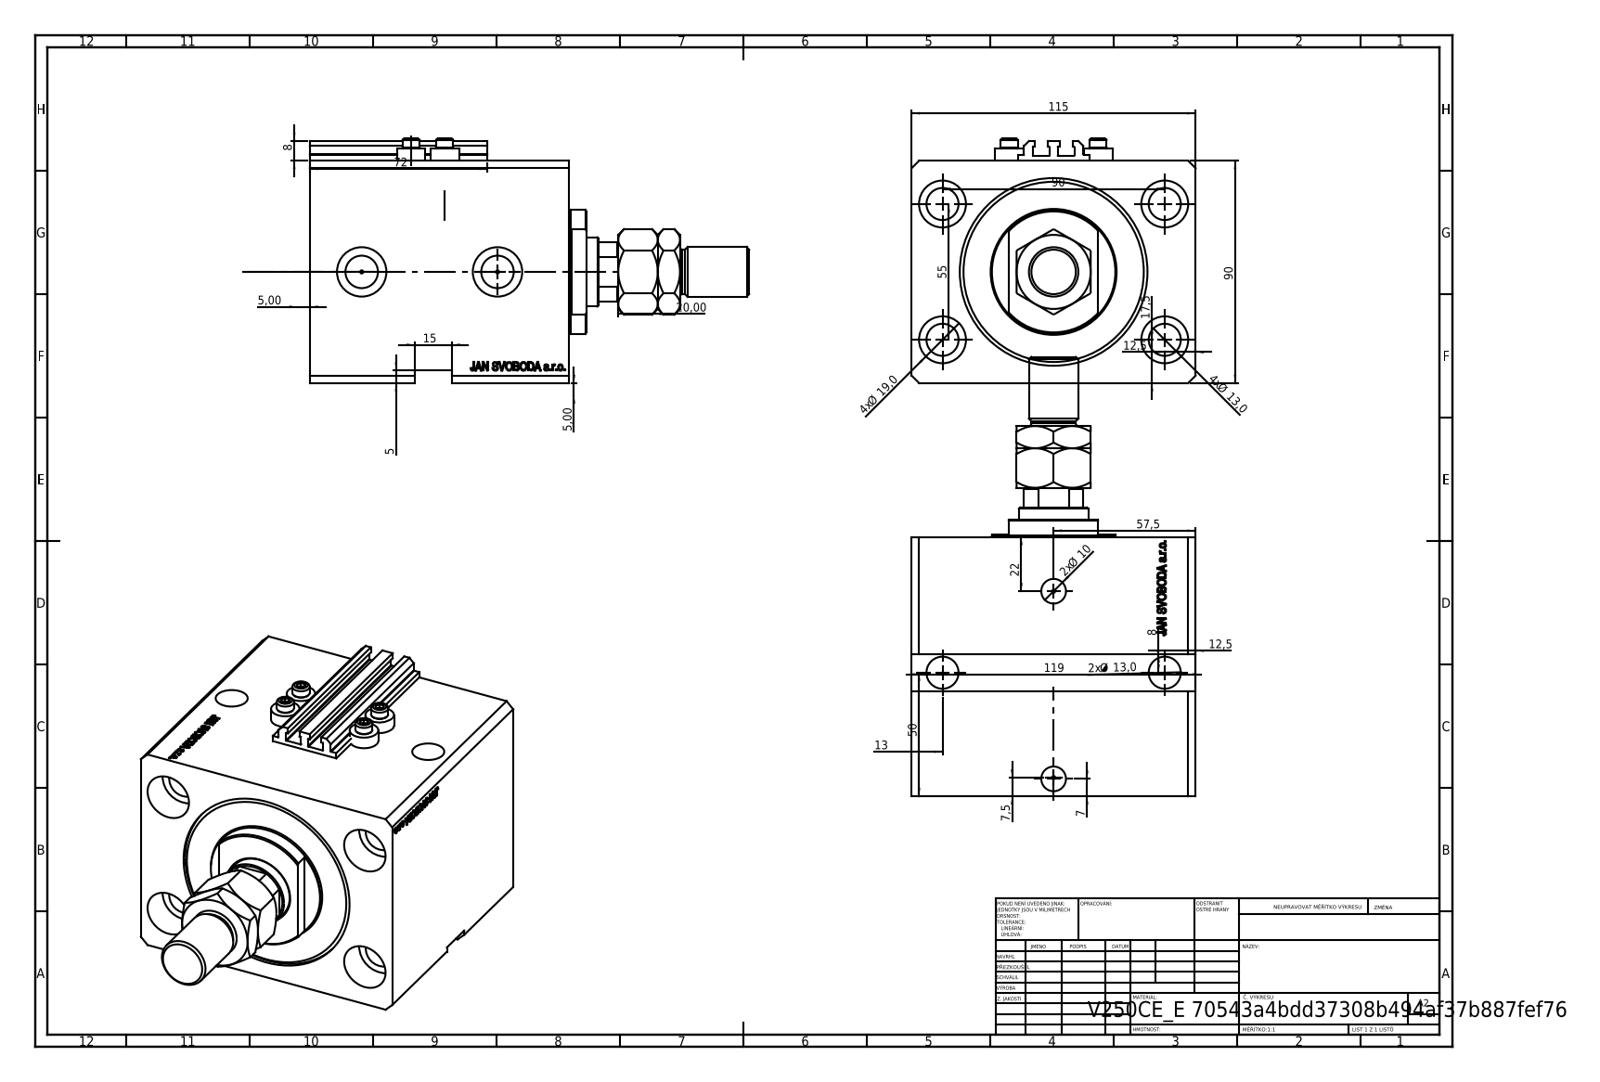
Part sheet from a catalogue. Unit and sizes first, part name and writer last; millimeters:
Units: millimetres
Overall size (bounding box): 177.9 × 115 × 99
Round holes (diameter × count): ⌀13 ×6, ⌀1.25 ×4, ⌀4 ×4, ⌀19 ×4, ⌀10 ×2, ⌀13.16 ×2, ⌀20 ×2, ⌀18.5 ×1, ⌀28 ×1, ⌀63 ×1, ⌀76 ×1
Round bosses / shafts (diameter × count): ⌀11.6 ×4, ⌀7 ×4, ⌀50 ×1, ⌀20 ×1, ⌀18 ×1
Partial cylindrical surfaces — rounded edges, fillets, slot ends (radius × count): R0.2 ×10, R13.5 ×1
Main face-to-face distances: 90, 115, 105, 87.1, 17.9, 57, 74.9, 30.1, 20, 54.9
Hole centre spacings: 52.74, 55, 90, 13.6, 27.39, 28.46, 33.62, 36
Volume: 982 434 mm³ · Surface area: 162 349 mm²
Bodies: 9 solids, 1156 faces (558 planar, 130 cylindrical, 468 other)
Part name (STEP PRODUCT): ALLEN BOLT V250CE; V250CE_VC_E; V250CE_E; MTA (+1 more)
STEP written by: SolidWorks 2019 (CONFIG_CONTROL_DESIGN)
